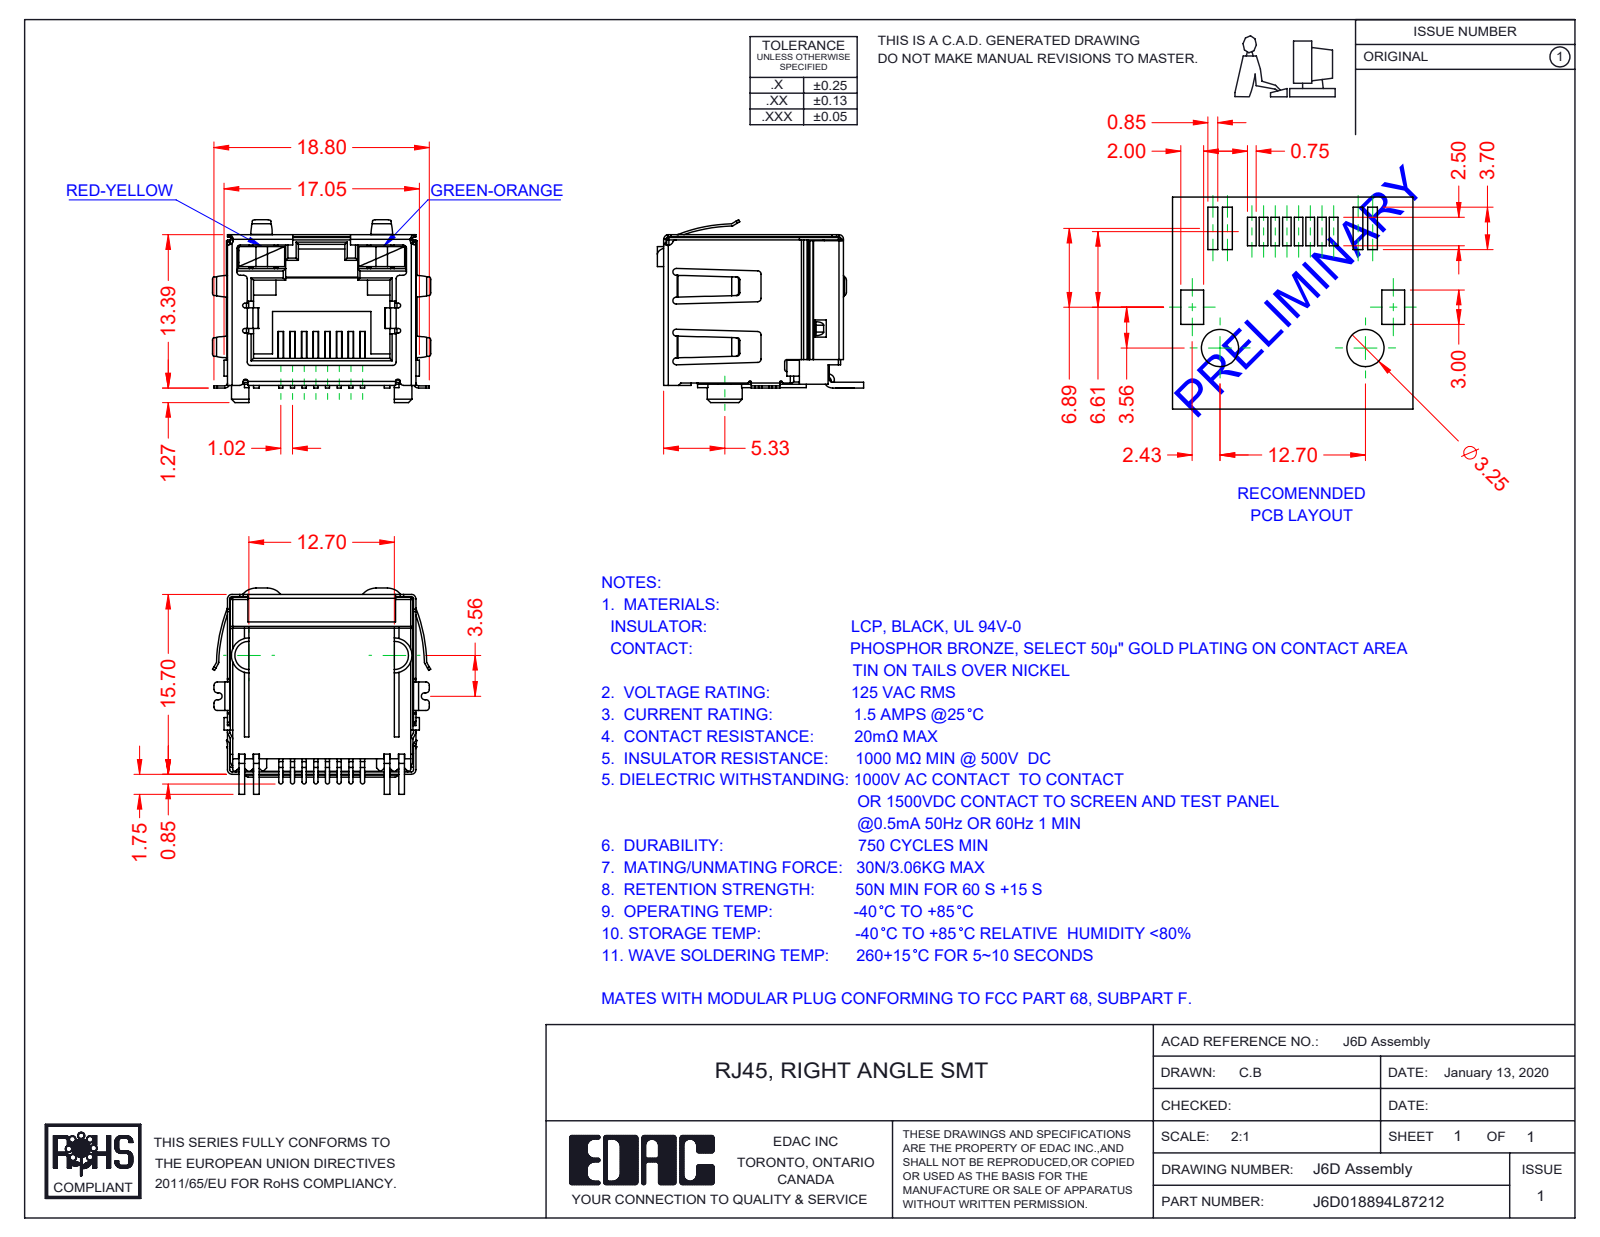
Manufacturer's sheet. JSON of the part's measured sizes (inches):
{"part_name": "6D LED LH_8-Red-Yellow; 6D Shield_LED - EMI; 6D LED RH_7-Green-Orange; 6D Contacts (+2 more)", "step_written_by": "SolidWorks 2016 (CONFIG_CONTROL_DESIGN)", "units": "inches", "bodies": {"solids": 12, "faces": 1034, "planar": 703, "cylindrical": 286, "other": 45}, "overall_size": [0.75, 0.709, 0.628], "volume_in3": 0.109, "surface_area_in2": 7.434, "partial_cylinders_radius": [[0.012, 55], [0.008, 40], [0.016, 19], [0.01, 16], [0.004, 12], [0.006, 8], [0.007, 8], [0.02, 6]], "face_to_face_distances": [0.63, 0.638, 0.64, 0.089, 0.039, 0.628, 0.504, 0.018, 0.514, 0.417]}
